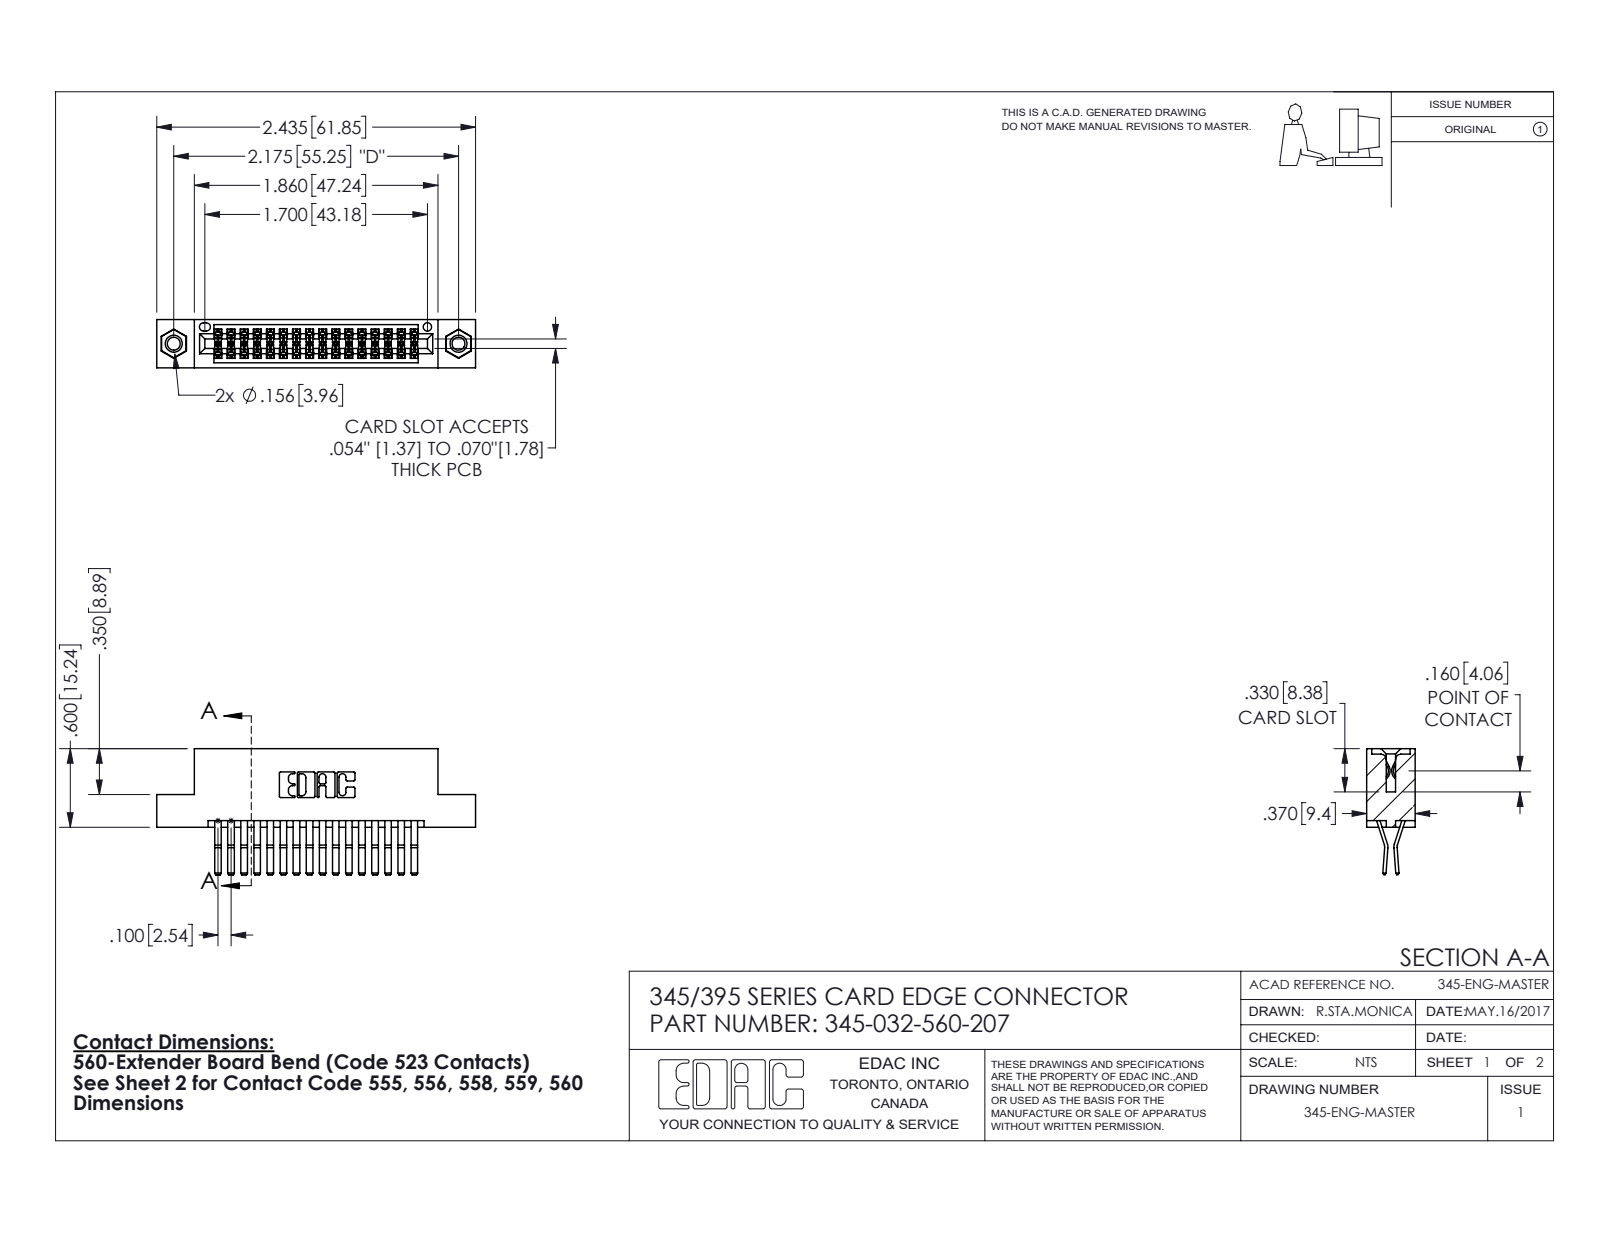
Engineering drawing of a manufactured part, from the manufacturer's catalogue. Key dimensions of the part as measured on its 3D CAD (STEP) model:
Part name (STEP PRODUCT): 345-250-001_345-250-005-103; 345-292-001_560 Tail; 345-032-560-207; 345 Part_Flush Mounting Lugs - 0.156 Dia-TI
STEP written by: SolidWorks 2016 (CONFIG_CONTROL_DESIGN)
Units: inches
Bodies: 35 solids, 1850 faces (1168 planar, 666 cylindrical, 16 other)
Overall size (bounding box): 2.435 × 0.962 × 0.37
Volume: 0.364 in³ · Surface area: 13.76 in²
Round holes (diameter × count): ⌀0.098 ×2, ⌀0.125 ×2, ⌀0.156 ×2, ⌀0.064 ×1
Round bosses / shafts (diameter × count): ⌀0.155 ×2
Partial cylindrical surfaces — rounded edges, fillets, slot ends (radius × count): R0.006 ×48, R0.01 ×22, R0.007 ×6, R0.031 ×6, R0.026 ×3, R0.01 ×2, R0.014 ×2, R0.019 ×2
Main face-to-face distances: 0.025, 0.072, 0.298, 0.2, 0.37, 0.098, 0.272, 0.225, 0.1, 0.175
Hole centre spacings: 0.27, 1.942, 2.175
